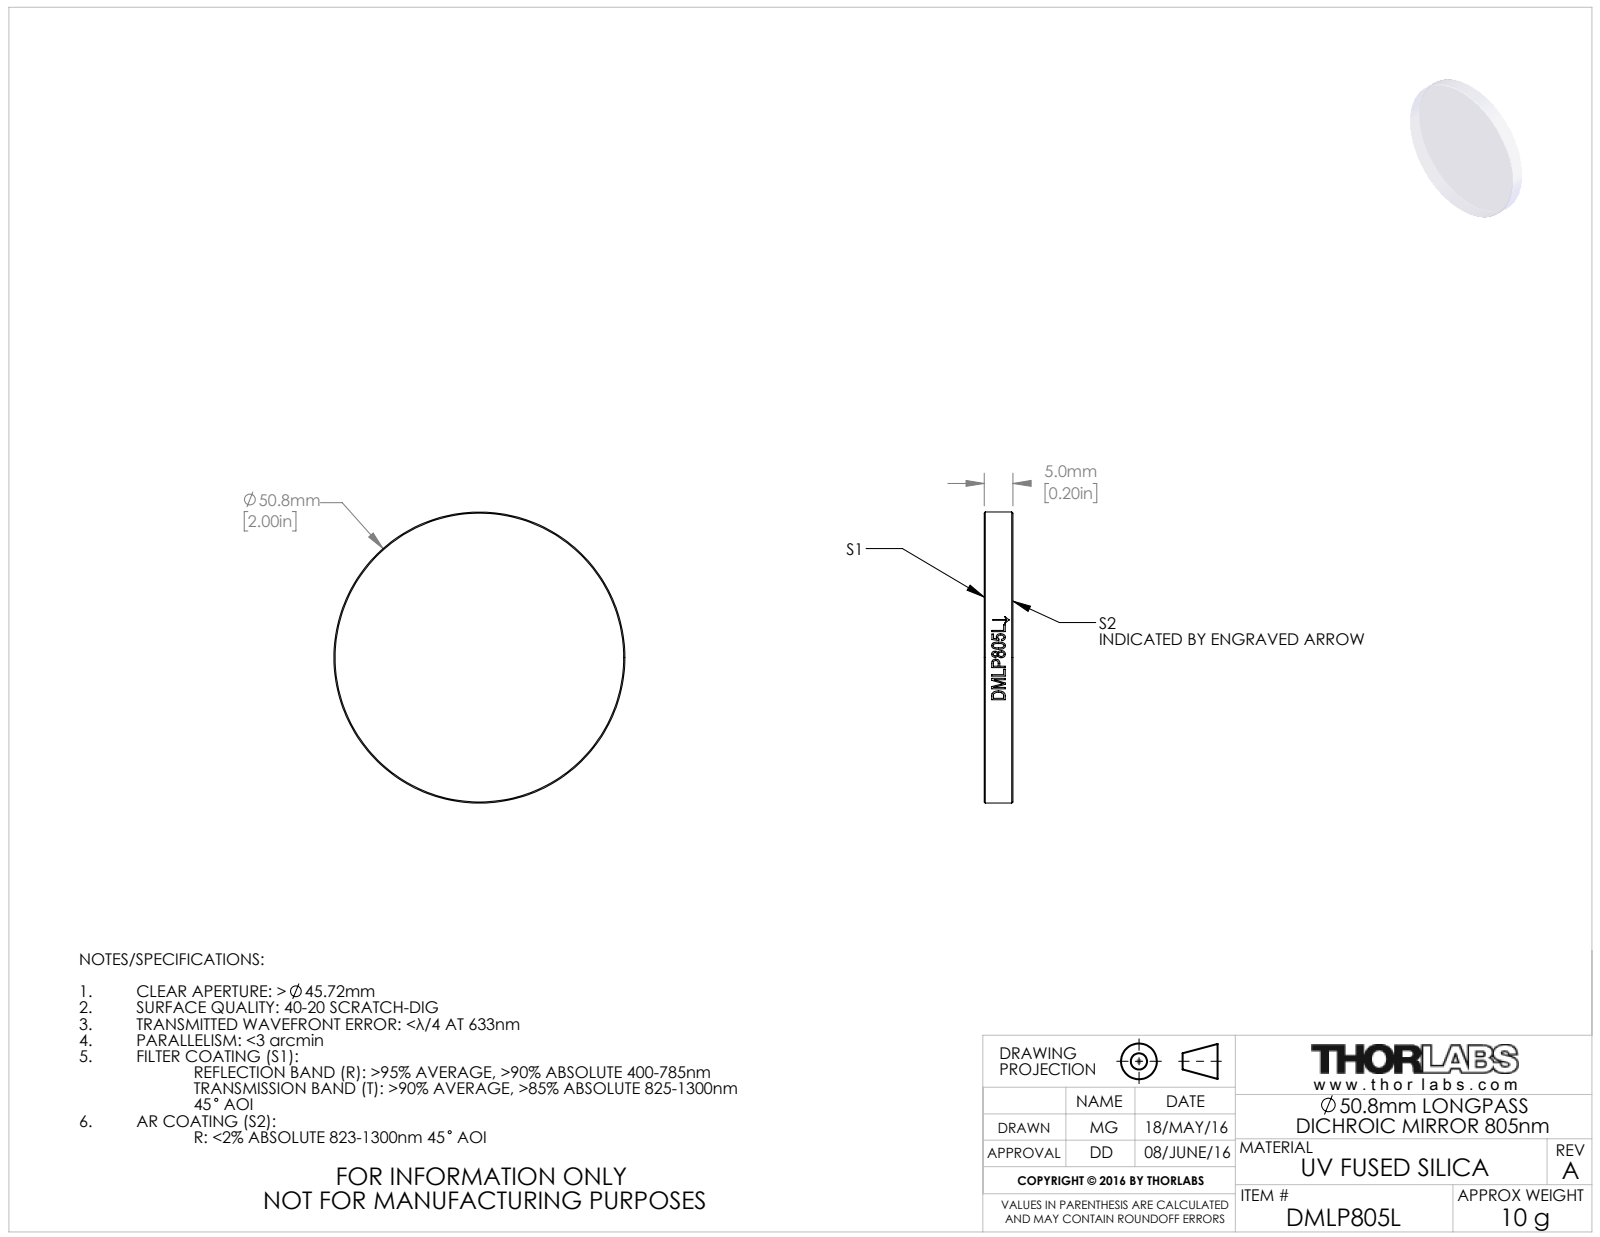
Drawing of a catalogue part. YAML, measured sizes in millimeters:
part_name: "TTN045170-E0W"
step_written_by: "SolidWorks 2016 (CONFIG_CONTROL_DESIGN)"
units: millimeters
bodies: {solids: 1, faces: 22, planar: 2, cylindrical: 16, other: 4}
overall_size: [50.8, 50.8, 5]
volume: 10129
surface_area: 4814
round_bosses_or_shafts:
  - {diameter: 50.8, count: 1}
face_to_face_distances: [5]
